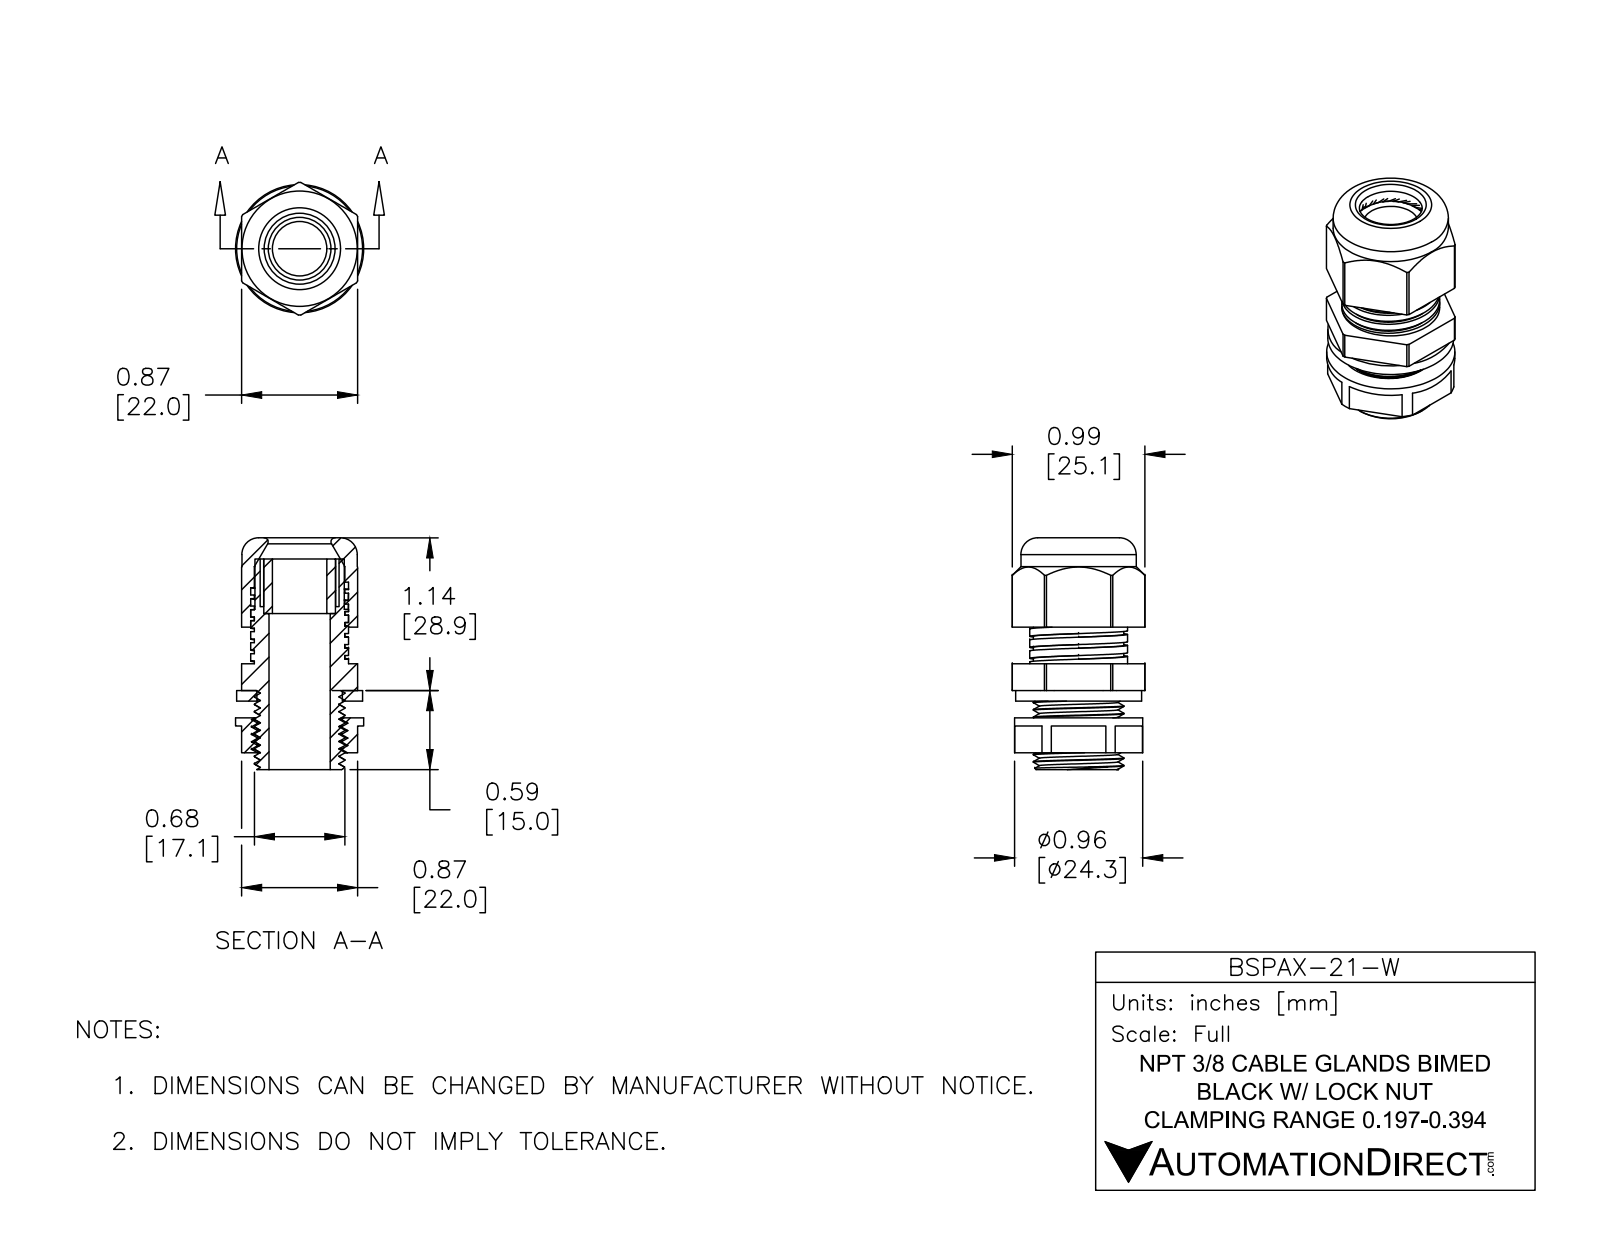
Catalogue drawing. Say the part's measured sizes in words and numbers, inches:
The part is named "BSPAX-21-W". Its 3-D file was written by "SolidWorks 2015 (CONFIG_CONTROL_DESIGN)". It is 5 solids with 236 faces: 127 planar, 85 cylindrical and 24 other. Overall it measures 1.73 by 0.99 by 0.957 inches. Its volume is 0.639 cubic inches and its surface area 18.98 square inches. Round holes: 1 of diameter 0.406, 1 of diameter 0.457, 1 of diameter 0.534, 1 of diameter 0.631, 1 of diameter 0.638, 1 of diameter 0.676. Round bosses or shafts: 1 of diameter 0.957, 1 of diameter 0.94, 1 of diameter 0.86, 1 of diameter 0.73, 1 of diameter 0.675, 1 of diameter 0.667. Partial cylindrical surfaces (rounded edges, fillets, slot ends): 1 of radius 0.495. The main face-to-face distances are 0.866, 0.02, 0.442, 0.462, 0.079, 0.464, 0.125, 0.204, 0.664, 0.2.
